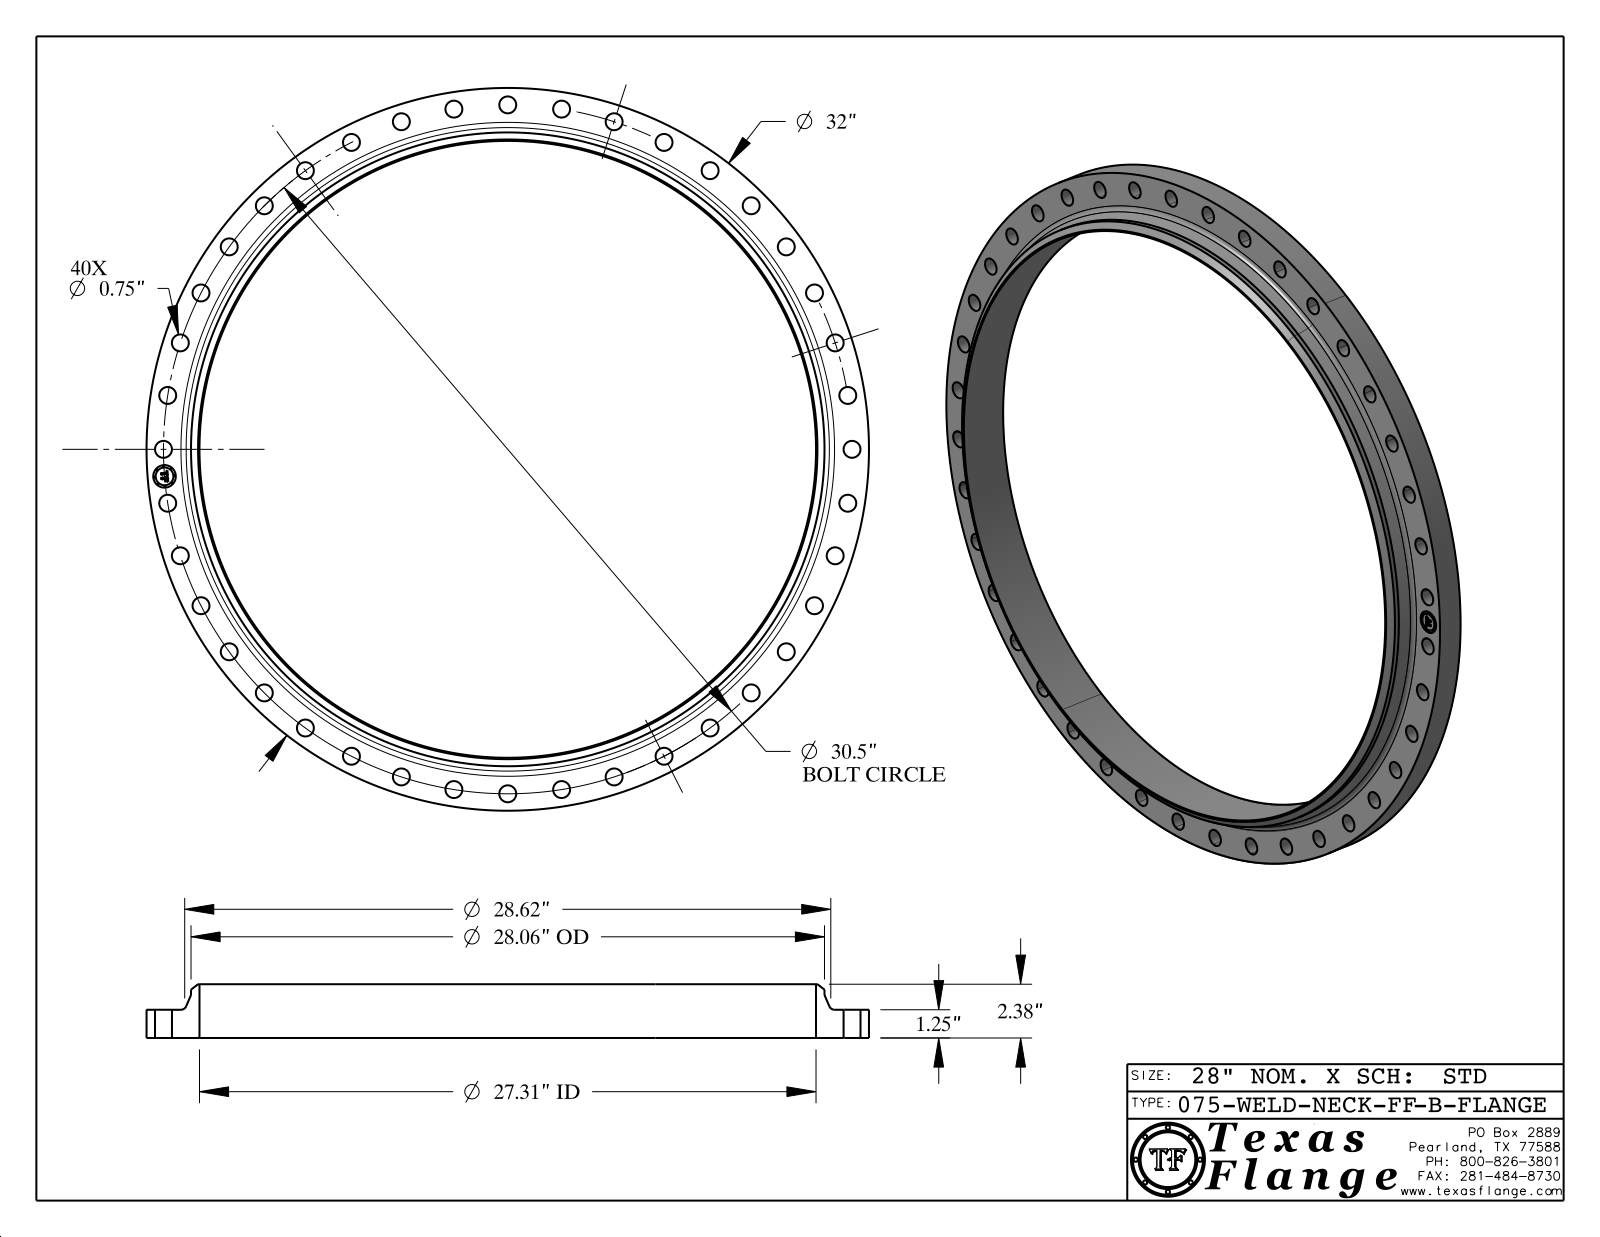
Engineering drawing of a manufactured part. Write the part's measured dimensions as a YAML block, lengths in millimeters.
part_name: "075-WELD-NECK-FF, Series B"
step_written_by: "CATIA V5 STEP AP214 (AUTOMOTIVE_DESIGN)"
units: millimeters
bodies: {solids: 1, faces: 480, planar: 368, cylindrical: 106, other: 6}
overall_size: [812.8, 812.8, 60.5]
volume: 4803000
surface_area: 588600
round_holes:
  - {diameter: 19.1, count: 40}
  - {diameter: 25.4, count: 1}
  - {diameter: 693.7, count: 1}
round_bosses_or_shafts:
  - {diameter: 1.5, count: 8}
  - {diameter: 812.8, count: 1}
  - {diameter: 712.7, count: 1}
  - {diameter: 20, count: 1}
face_to_face_distances: [31.8, 60.5, 28.7, 31.4, 0.4, 29.1, 7.6, 7.4, 1.4, 4.9]
hole_center_spacings: [387.4, 772.3, 765.1, 121.2, 736.8, 715.7, 180.8, 660.6]
